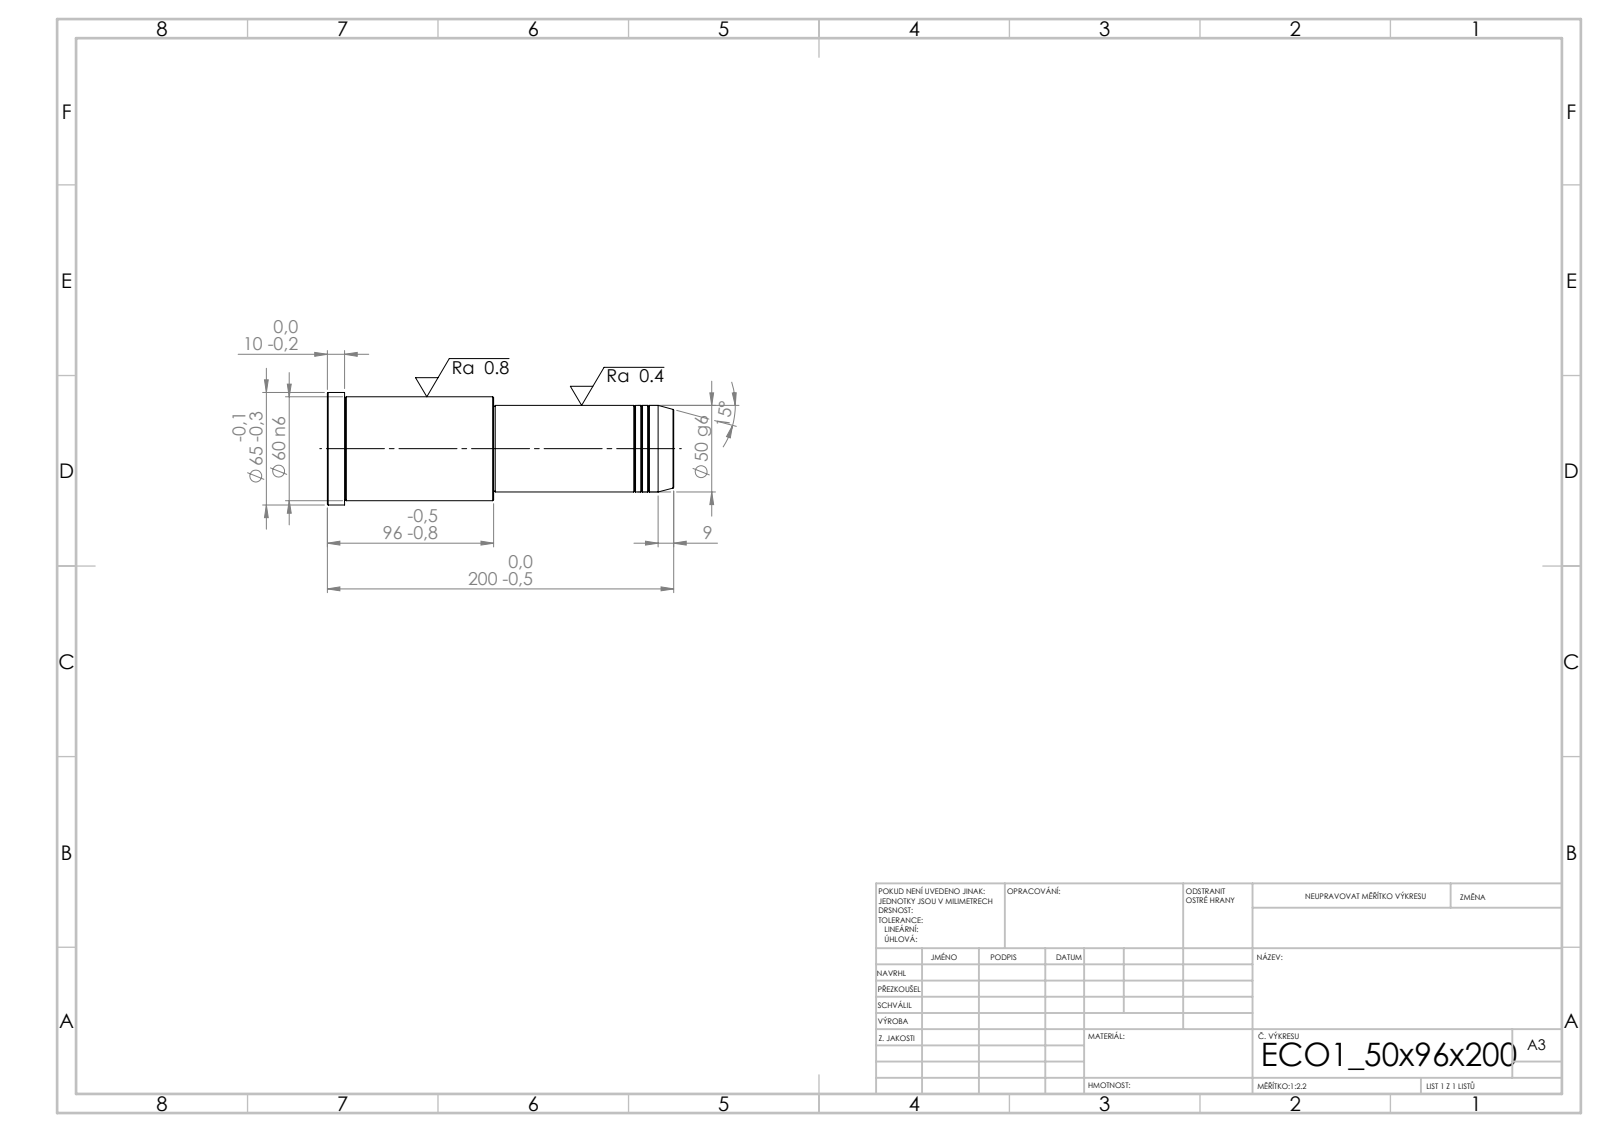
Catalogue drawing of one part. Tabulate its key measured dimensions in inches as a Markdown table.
| quantity | value |
| --- | --- |
| STEP written by | SolidWorks 2019 (CONFIG_CONTROL_DESIGN) |
| units | inches |
| bodies | 1 solid, 43 faces (5 planar, 14 cylindrical, 24 other) |
| overall size | 7.874 × 2.559 × 2.559 |
| volume | 29.2 in³ |
| surface area | 63.91 in² |
| round bosses / shafts (diameter × count) | 2.559 × 1, 2.362 × 1, 1.969 × 1, 1.929 × 1 |
| main face-to-face distances | 7.874, 4.094, 3.78, 7.48, 3.386, 0.394, 4.055, 0.039, 3.425, 3.819 |
